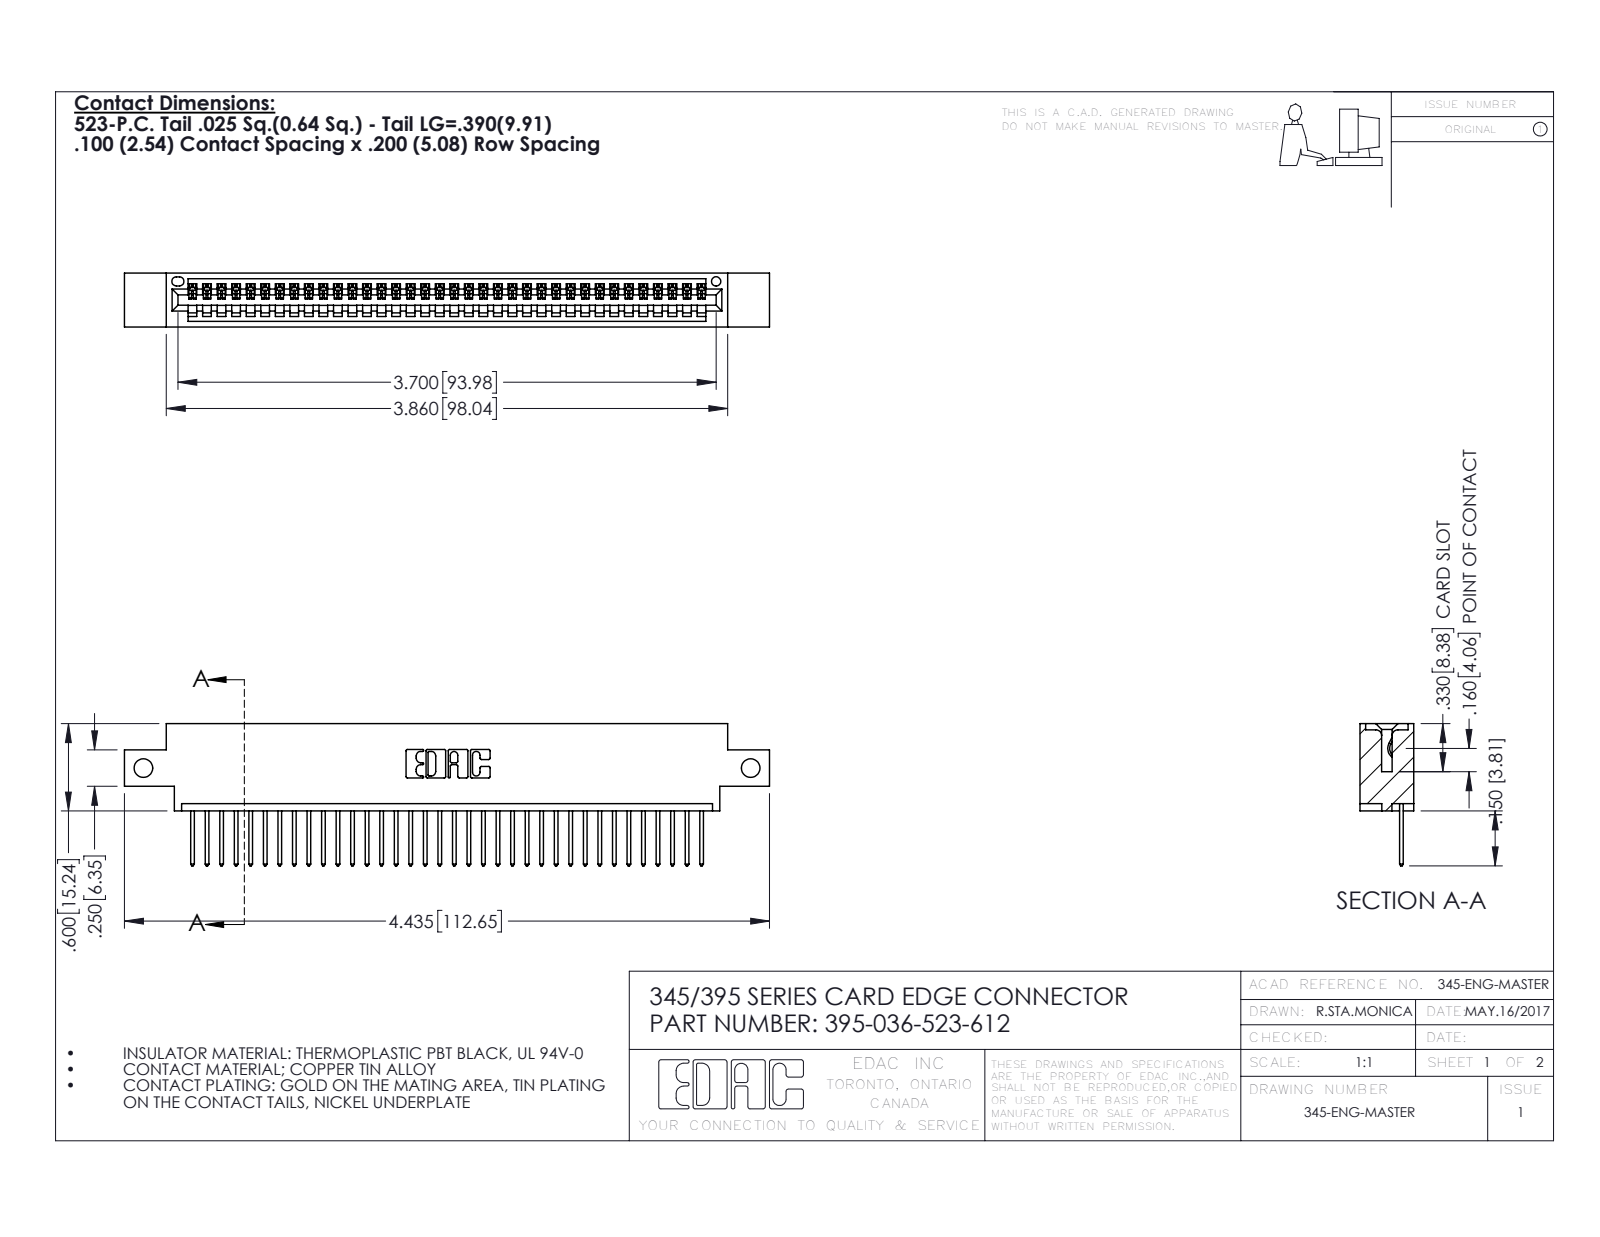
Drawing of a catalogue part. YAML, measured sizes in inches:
part_name: "345 Part_0.170 Offset - Side Mount; 395-036-523-612; 345-292-001_345-293-123"
step_written_by: "SolidWorks 2016 (CONFIG_CONTROL_DESIGN)"
units: inches
bodies: {solids: 37, faces: 2218, planar: 1524, cylindrical: 694, other: 0}
overall_size: [4.435, 0.977, 0.37]
volume: 0.637
surface_area: 21.41
round_holes:
  - {diameter: 0.128, count: 2}
  - {diameter: 0.064, count: 1}
partial_cylinders:
  - {radius: 0.006, count: 72}
  - {radius: 0.01, count: 72}
  - {radius: 0.01, count: 22}
  - {radius: 0.007, count: 6}
  - {radius: 0.031, count: 6}
  - {radius: 0.026, count: 3}
  - {radius: 0.031, count: 2}
  - {radius: 0.04, count: 2}
face_to_face_distances: [0.298, 0.072, 0.37, 0.2, 0.098, 0.272, 0.025, 0.225, 0.175, 0.149]
hole_center_spacings: [4.175]
